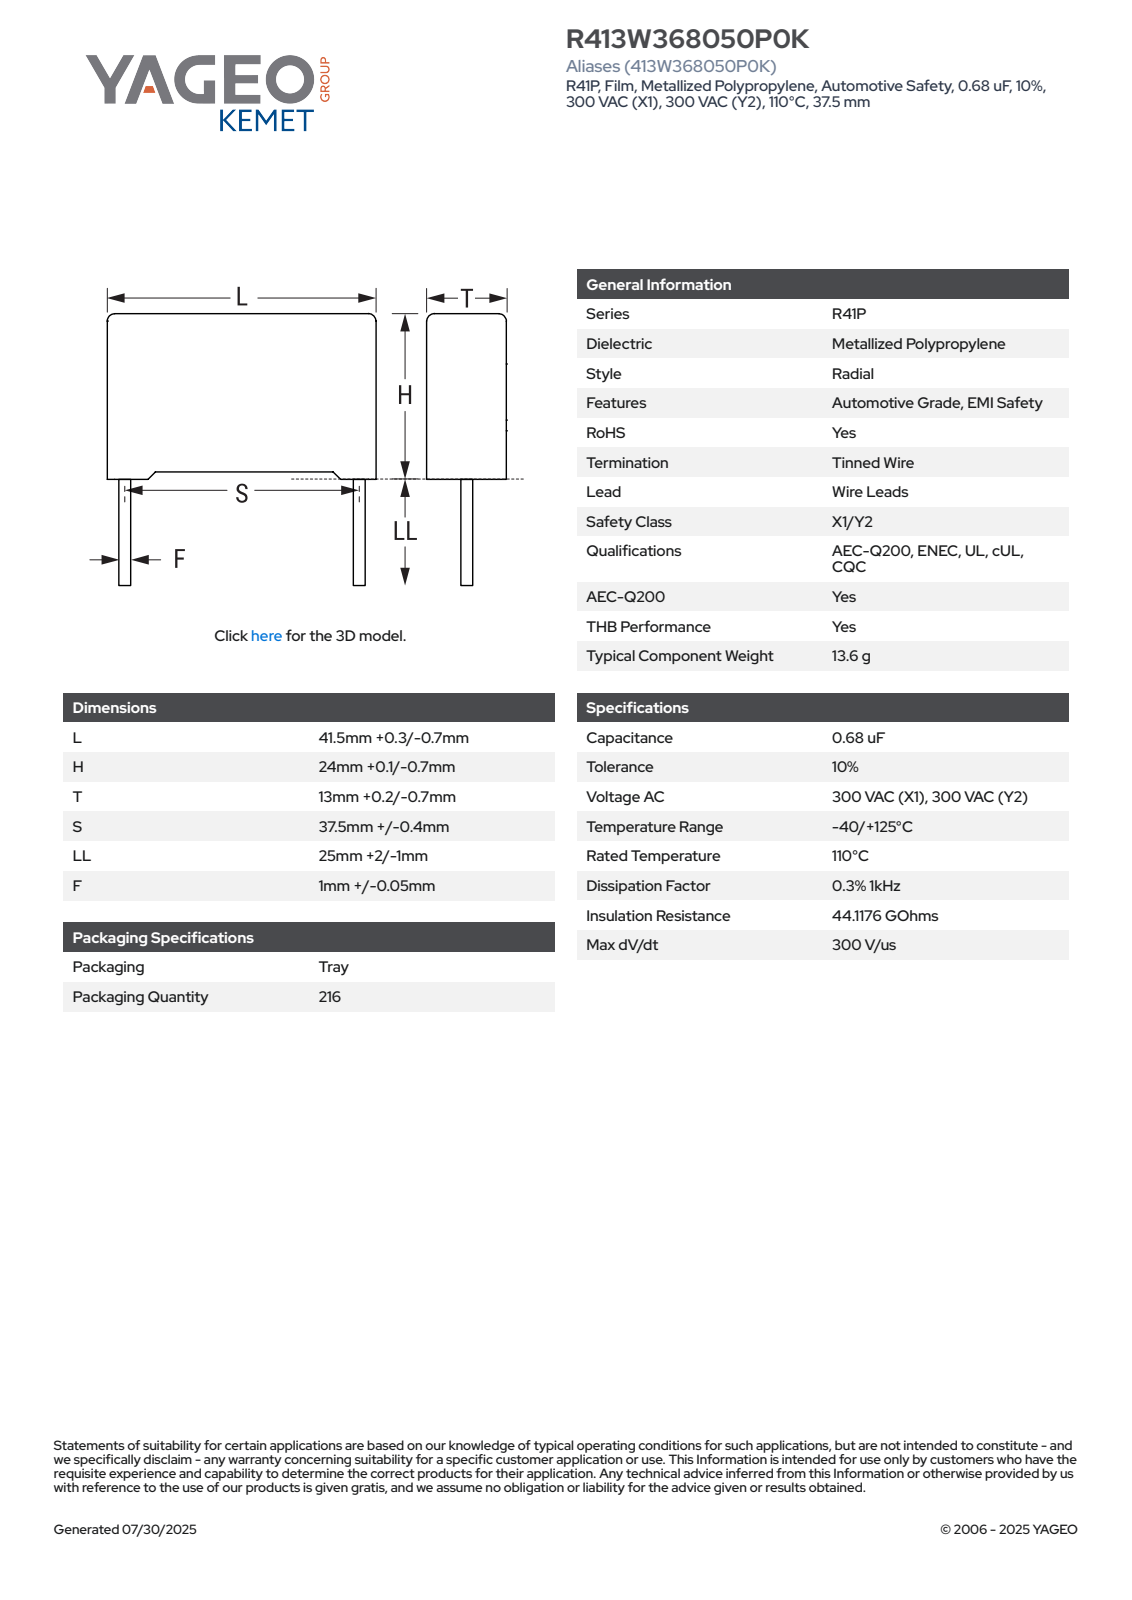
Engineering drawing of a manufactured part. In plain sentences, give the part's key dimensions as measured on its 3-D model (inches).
The part is named "CFR_RB2_41.5X24X13_L41.8H24.1T13.2S37.5LL27F1.05". Its 3-D file was written by "SolidWorks 2021 (AUTOMOTIVE_DESIGN)". It is 4 solids with 85 faces: 77 planar, 8 cylindrical and 0 other. Overall it measures 2.012 by 1.646 by 0.52 inches. Its volume is 0.789 cubic inches and its surface area 6.223 square inches. Round bosses or shafts: 2 of diameter 0.041. Partial cylindrical surfaces (rounded edges, fillets, slot ends): 4 of radius 0.02. The main face-to-face distances are 0.52, 0.916, 1.646, 0.919, 0.03, 0.033, 0.949, 0.52, 0.055, 1.591.
